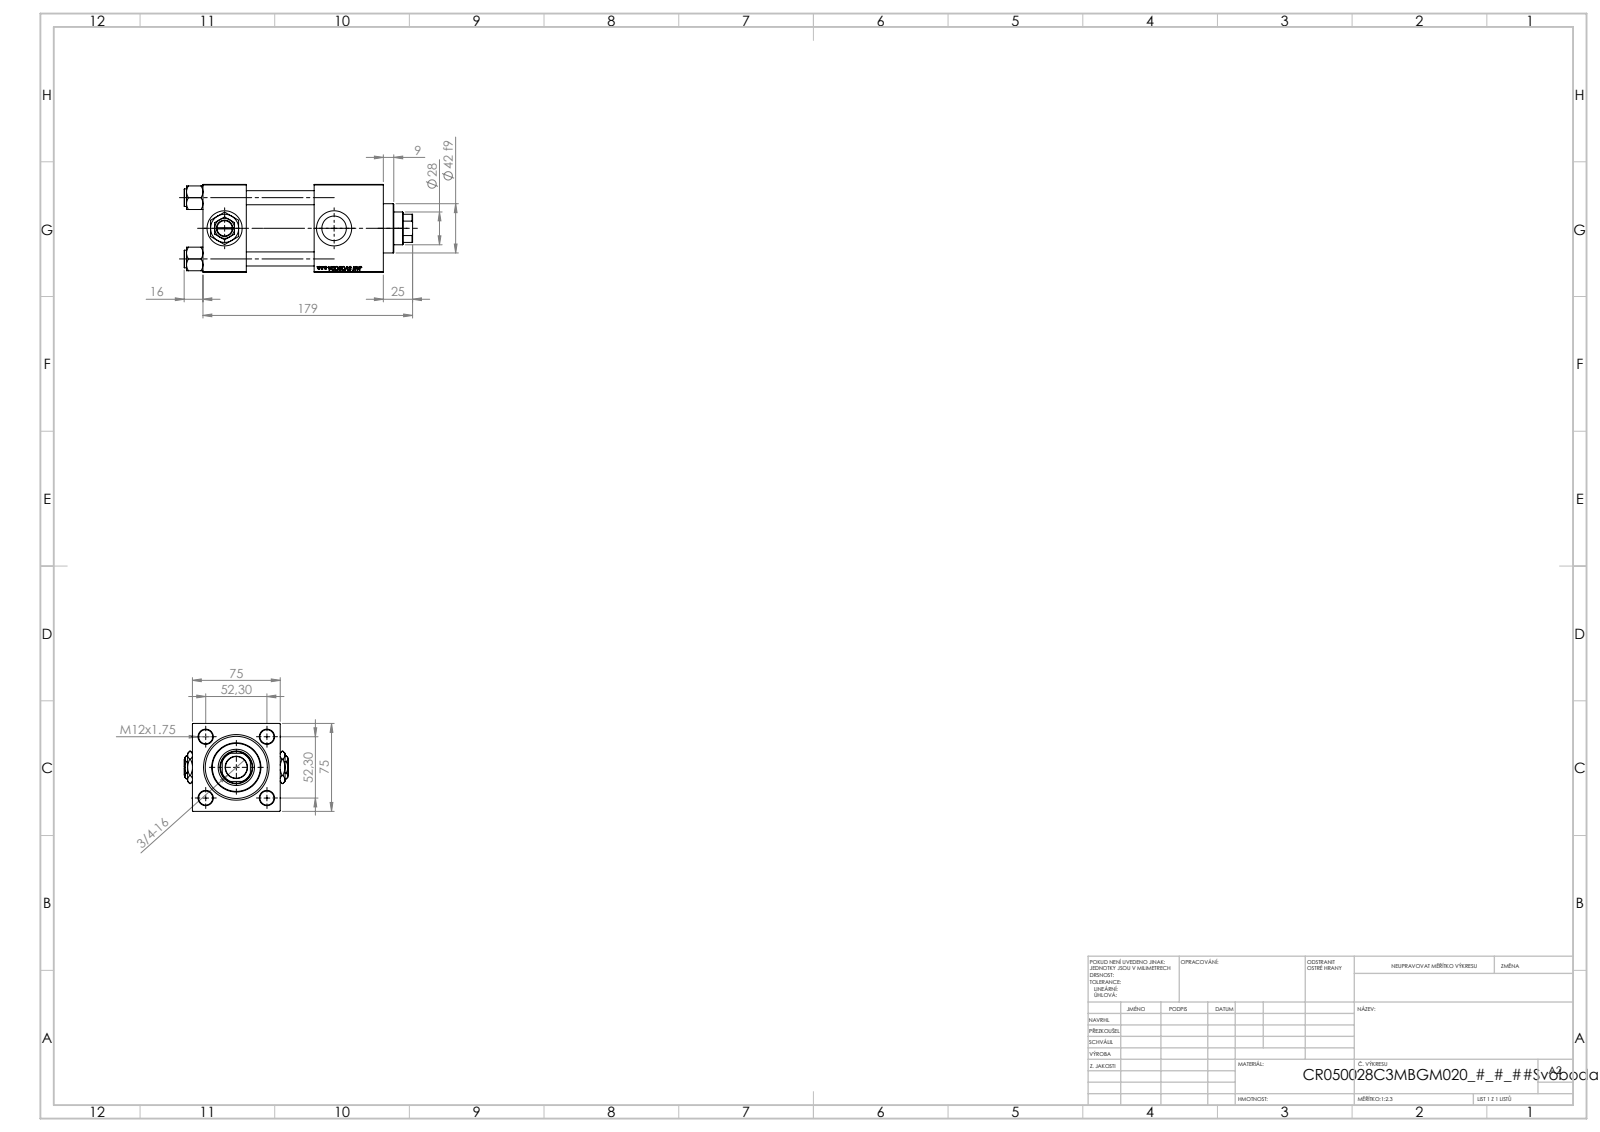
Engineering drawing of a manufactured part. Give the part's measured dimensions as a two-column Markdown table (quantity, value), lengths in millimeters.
| quantity | value |
| --- | --- |
| part name | V215CR_C_Body; V215_VC_A; V215CR_C_TYCINKA; V215CR_VCP_C (+2 more) |
| STEP written by | SolidWorks 2019 (CONFIG_CONTROL_DESIGN) |
| units | millimeters |
| bodies | 13 solids, 1249 faces (573 planar, 98 cylindrical, 578 other) |
| overall size | 195 × 89 × 75 |
| volume | 663 959 mm³ |
| surface area | 155 409 mm² |
| round holes (diameter × count) | 12 × 4, 7 × 2, 20.96 × 2, 30 × 2, 18.5 × 1, 28 × 1, 31 × 1, 41 × 1, 50 × 1, 53 × 1 |
| round bosses / shafts (diameter × count) | 15 × 4, 56 × 1, 42 × 1 |
| partial cylindrical surfaces (radius × count) | 13.5 × 1 |
| main face-to-face distances | 75, 37, 154, 117, 95, 58, 59, 125.3, 88.3, 30.3 |
| hole center spacings | 36.98, 52.3, 73.96, 93.5 |
